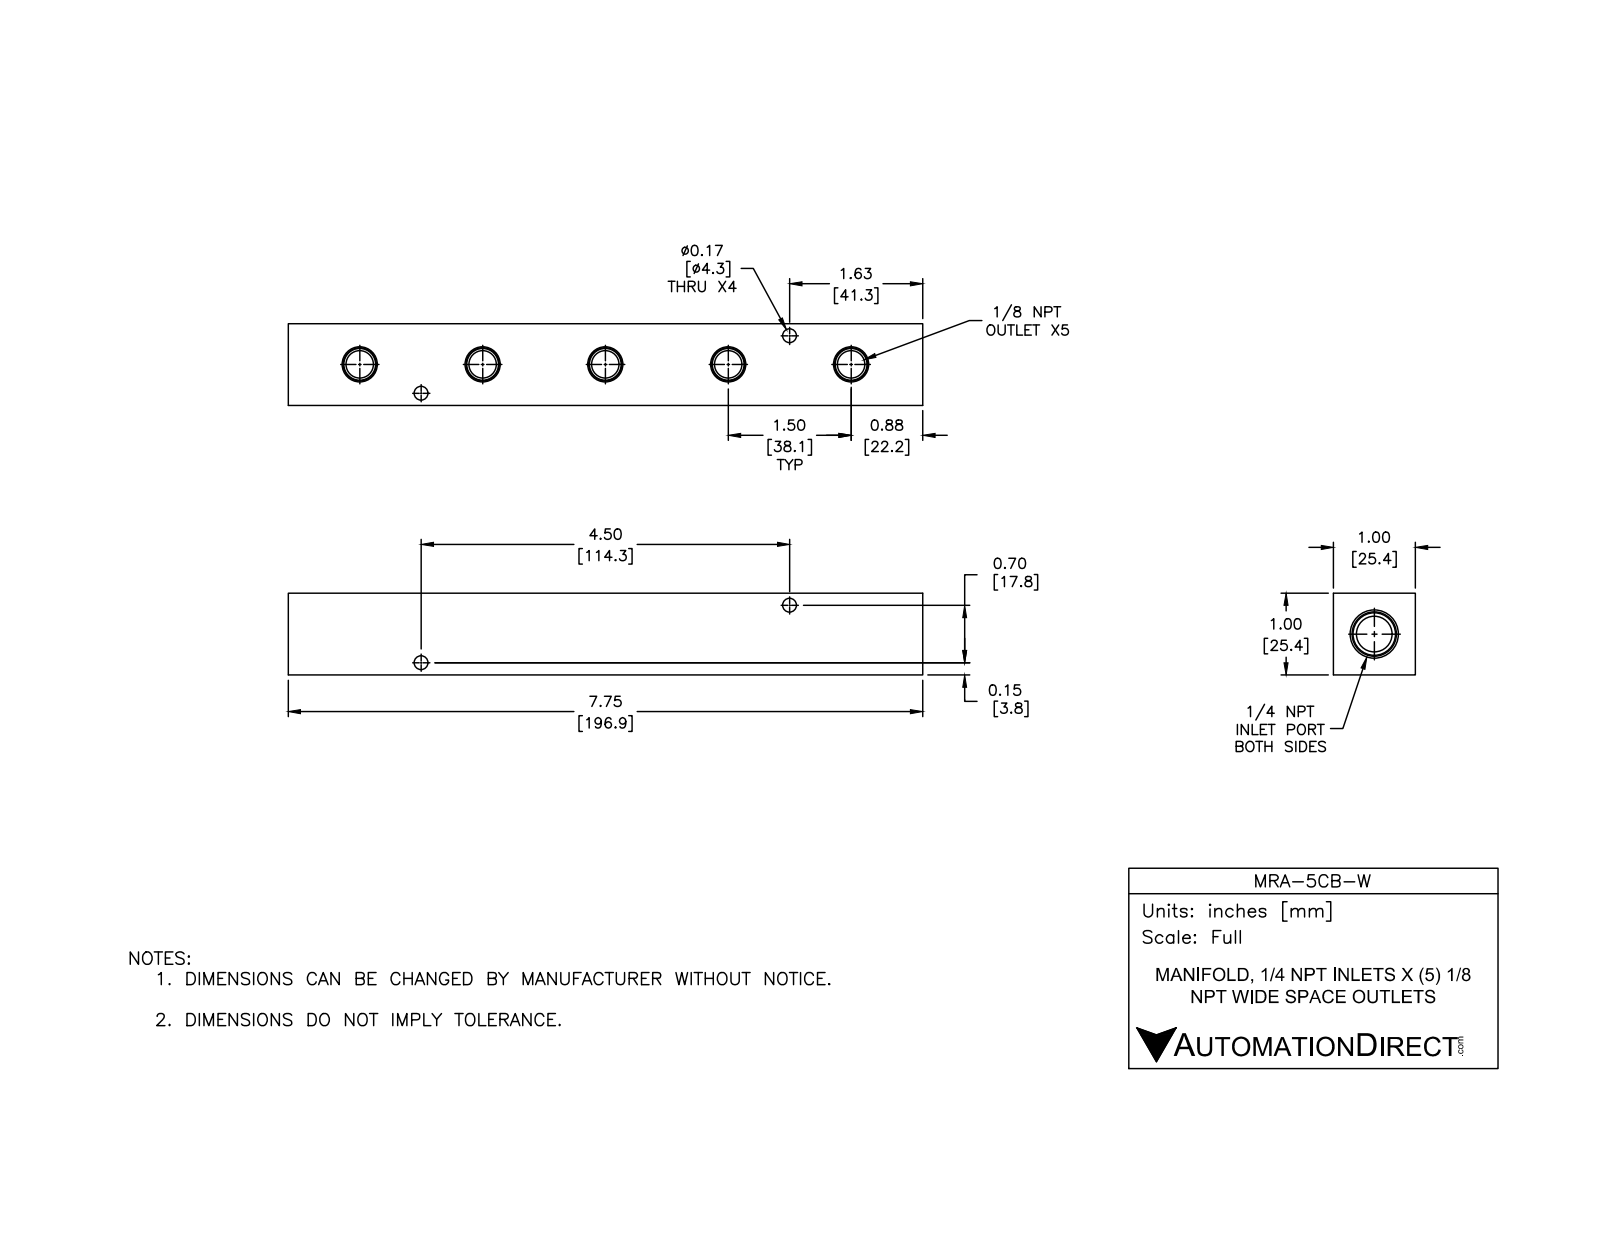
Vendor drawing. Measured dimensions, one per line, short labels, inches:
name: MRA-5CB-W
written by: SolidWorks 2015 (CONFIG_CONTROL_DESIGN)
unit: in
bodies: 1 solid, 69 faces (13 planar, 28 cylindrical, 28 other)
size: 7.75 × 1 × 1
volume: 6.262 in³; area: 46.16 in²
holes: 5× ⌀0.332, 4× ⌀0.17, 1× ⌀0.438
face distances: 1, 7.75, 0.73, 0.27, 0.39, 7.36, 6.97
hole spacings: 0.828, 1.5, 3, 2.277, 3.766, 4.5, 4.554, 5.262
